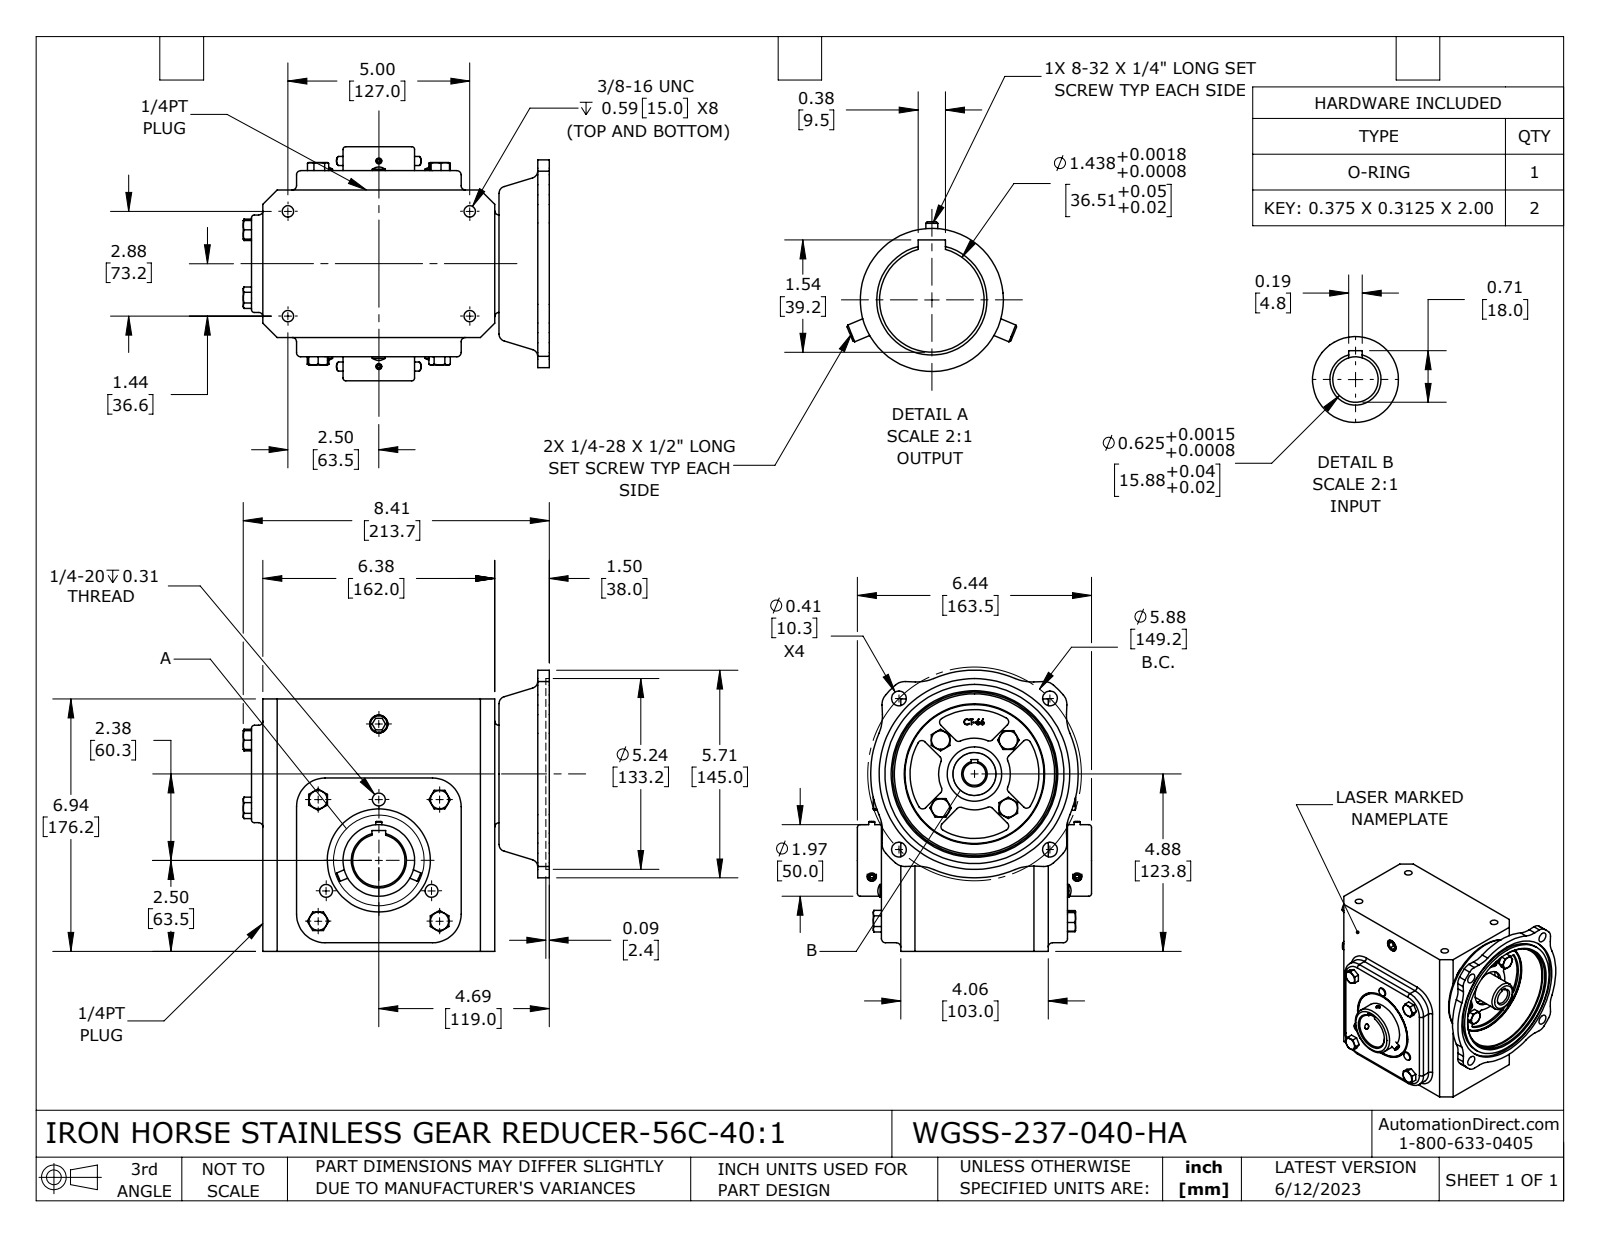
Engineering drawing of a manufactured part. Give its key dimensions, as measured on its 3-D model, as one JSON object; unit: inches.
{"part_name": "WGSS-237-040-HA", "step_written_by": "SolidWorks 2021 (CONFIG_CONTROL_DESIGN)", "units": "inches", "bodies": {"solids": 7, "faces": 670, "planar": 287, "cylindrical": 195, "other": 188}, "overall_size": [8.412, 7.729, 6.437], "volume_in3": 204.5, "surface_area_in2": 348.1, "round_holes": [[0.213, 4], [0.313, 4], [0.406, 4], [0.136, 2], [0.625, 1], [0.866, 1], [1.437, 1], [1.441, 1], [1.496, 1], [1.772, 1], [3.819, 1], [4.5, 1]], "round_bosses_or_shafts": [[0.25, 4], [0.354, 3], [0.164, 2], [4.921, 1], [2.835, 1], [1.969, 1], [1.181, 1]], "partial_cylinders_radius": [[0.118, 40], [0.394, 12], [1.181, 8], [0.079, 4], [0.787, 4], [0.984, 1], [1.772, 1], [2.854, 1]], "face_to_face_distances": [0.531, 4.587, 6.937, 0.315, 4.055, 6.378, 5.118, 7.874, 1.181, 6.693], "hole_center_spacings": [2.858, 2.937, 4.944, 5.65, 2.88, 4.154, 4.154, 5]}
